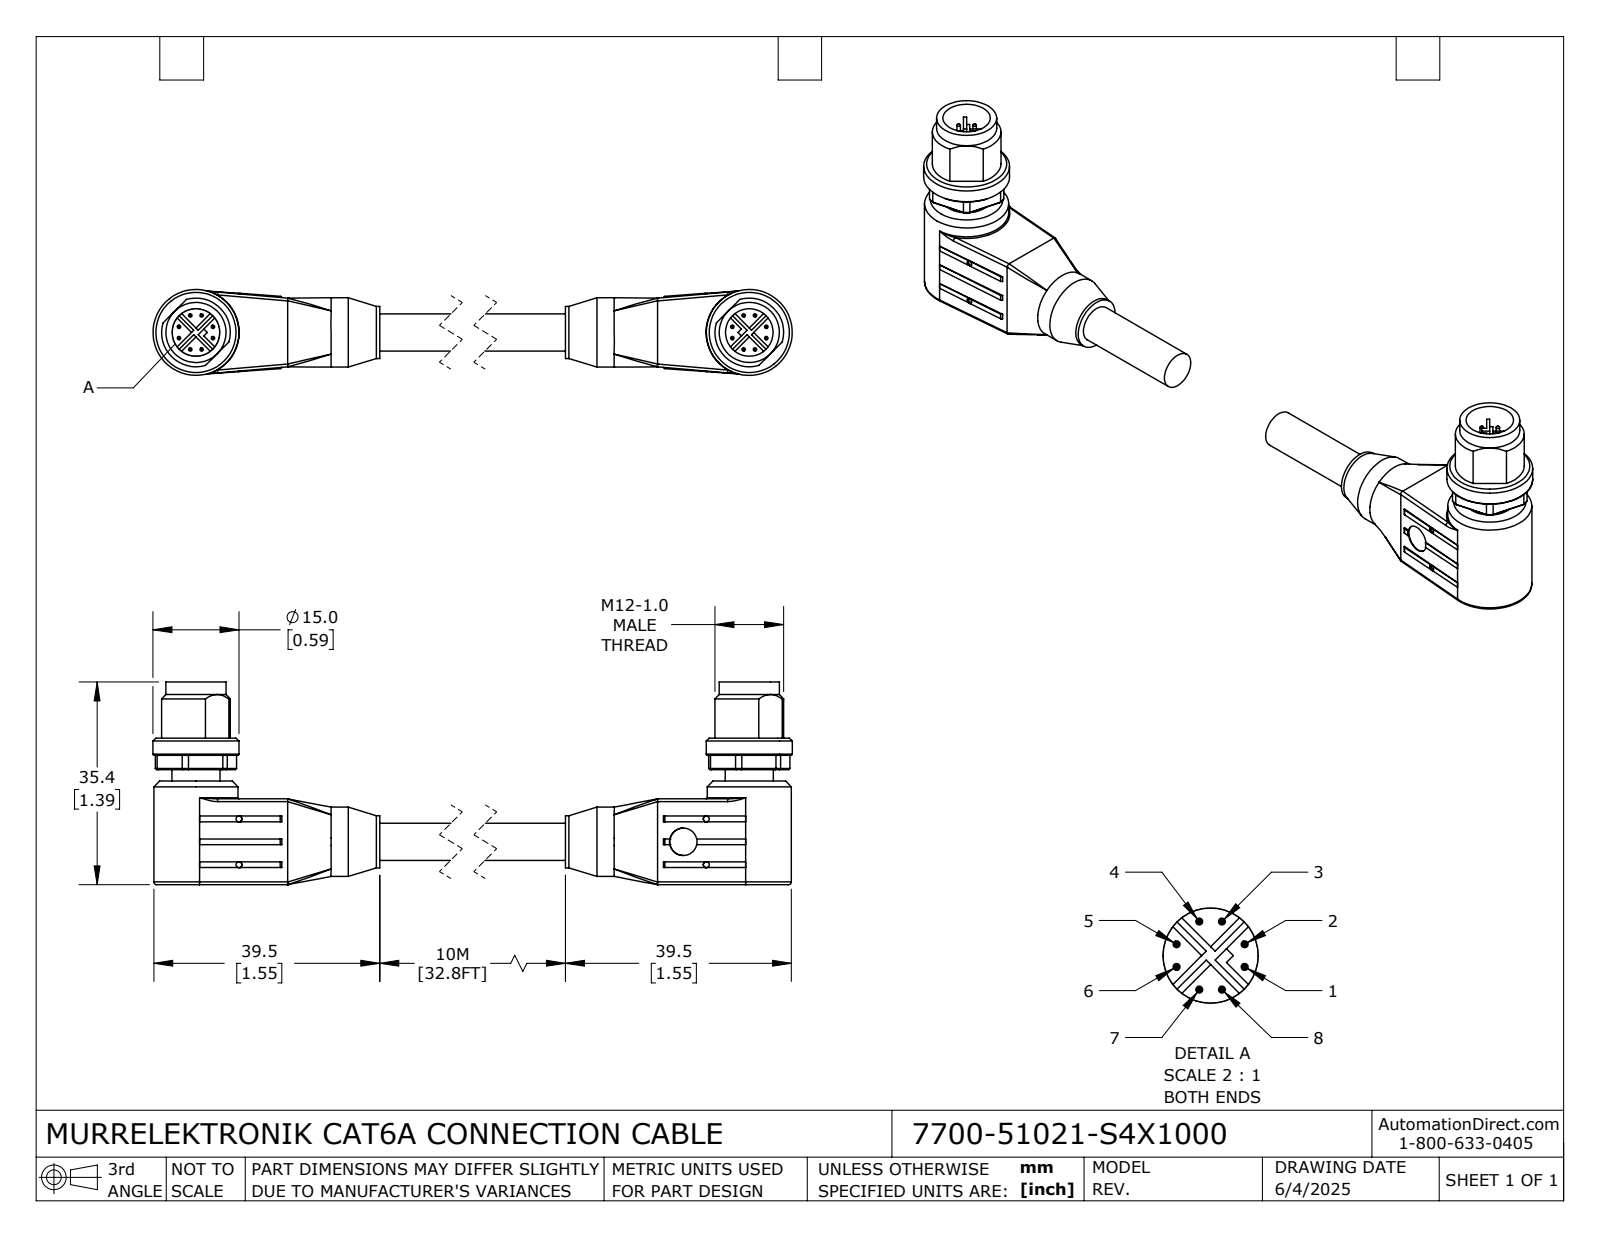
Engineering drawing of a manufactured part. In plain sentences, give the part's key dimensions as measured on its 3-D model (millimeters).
The part is named "7700-51021-S4X1000_MALE; 7700-51021-S4X1000". Its 3-D file was written by "SolidWorks 2024 (CONFIG_CONTROL_DESIGN)". It is 2 solids with 424 faces: 196 planar, 134 cylindrical and 94 other. Overall it measures 144.2 by 35.4 by 15 millimeters. Its volume is 18 415 cubic millimeters and its surface area 8 016 square millimeters. Round holes: 8 of diameter 1.05, 2 of diameter 4.8, 2 of diameter 8.3. Round bosses or shafts: 16 of diameter 0.6, 2 of diameter 15, 2 of diameter 14.7, 2 of diameter 10.5, 2 of diameter 8.4, 1 of diameter 12.1, 1 of diameter 9.1, 1 of diameter 6.5. Partial cylindrical surfaces (rounded edges, fillets, slot ends): 8 of radius 0.5, 4 of radius 0.3, 2 of radius 6, 2 of radius 7.2. The main face-to-face distances are 3.59, 15, 91.34, 20.1, 5.1, 18.1, 3.1, 2, 1.1, 4.7. The hole center spacings are 8, 114.84, 115.12, 106.88, 129.2.
